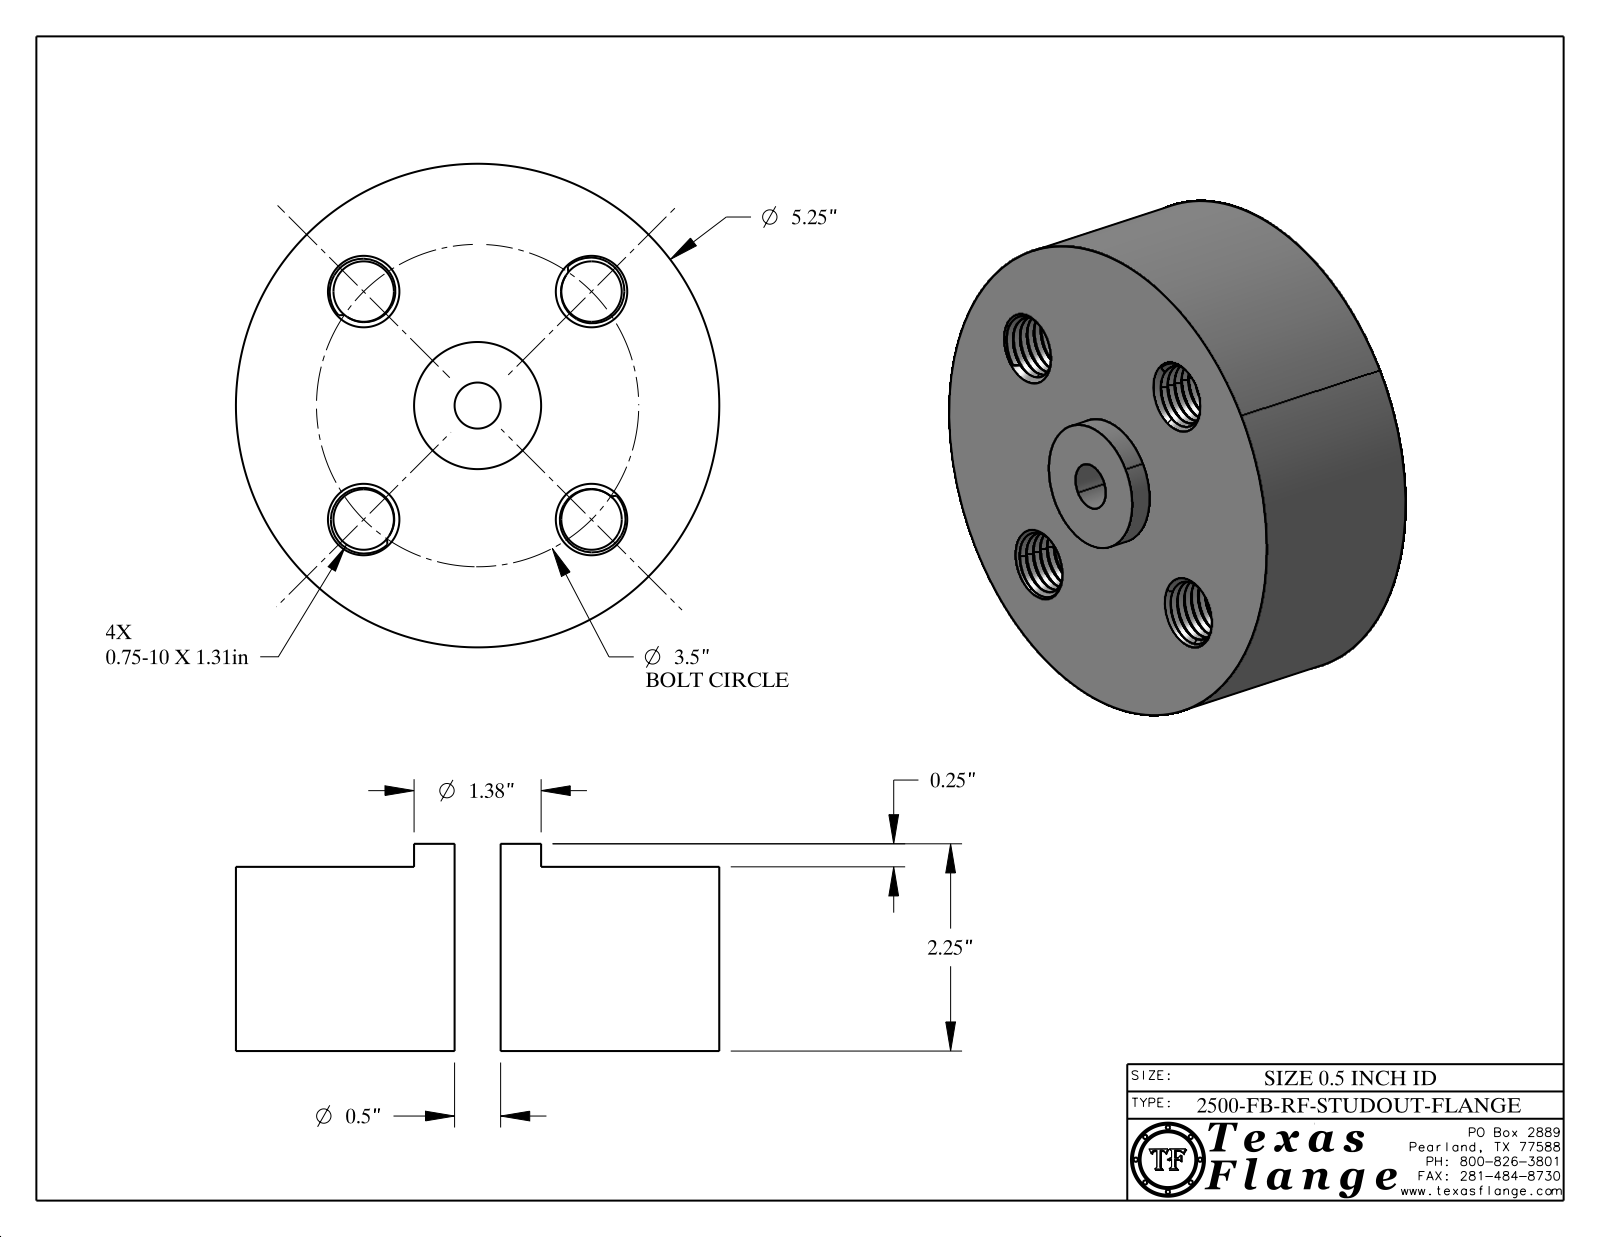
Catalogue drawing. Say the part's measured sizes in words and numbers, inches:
The part is named "0.5-2500-FB-RF-STUDOUT-FLANGE". Its 3-D file was written by "CATIA V5 STEP AP214 (AUTOMOTIVE_DESIGN)". It is 1 solid with 634 faces: 368 planar, 106 cylindrical and 160 other. Overall it measures 5.25 by 5.25 by 2.25 inches. Its volume is 41.19 cubic inches and its surface area 94.49 square inches. Round holes: 4 of diameter 0.656, 1 of diameter 0.5, 1 of diameter 1. Round bosses or shafts: 8 of diameter 0.061, 1 of diameter 5.25, 1 of diameter 1.38, 1 of diameter 0.788. The main face-to-face distances are 2, 0.25, 2.25, 2.235, 1.985, 0.015, 0.298, 0.293, 0.054, 0.248. The hole center spacings are 1.75, 2.475, 1.339, 3.233, 3.5.
